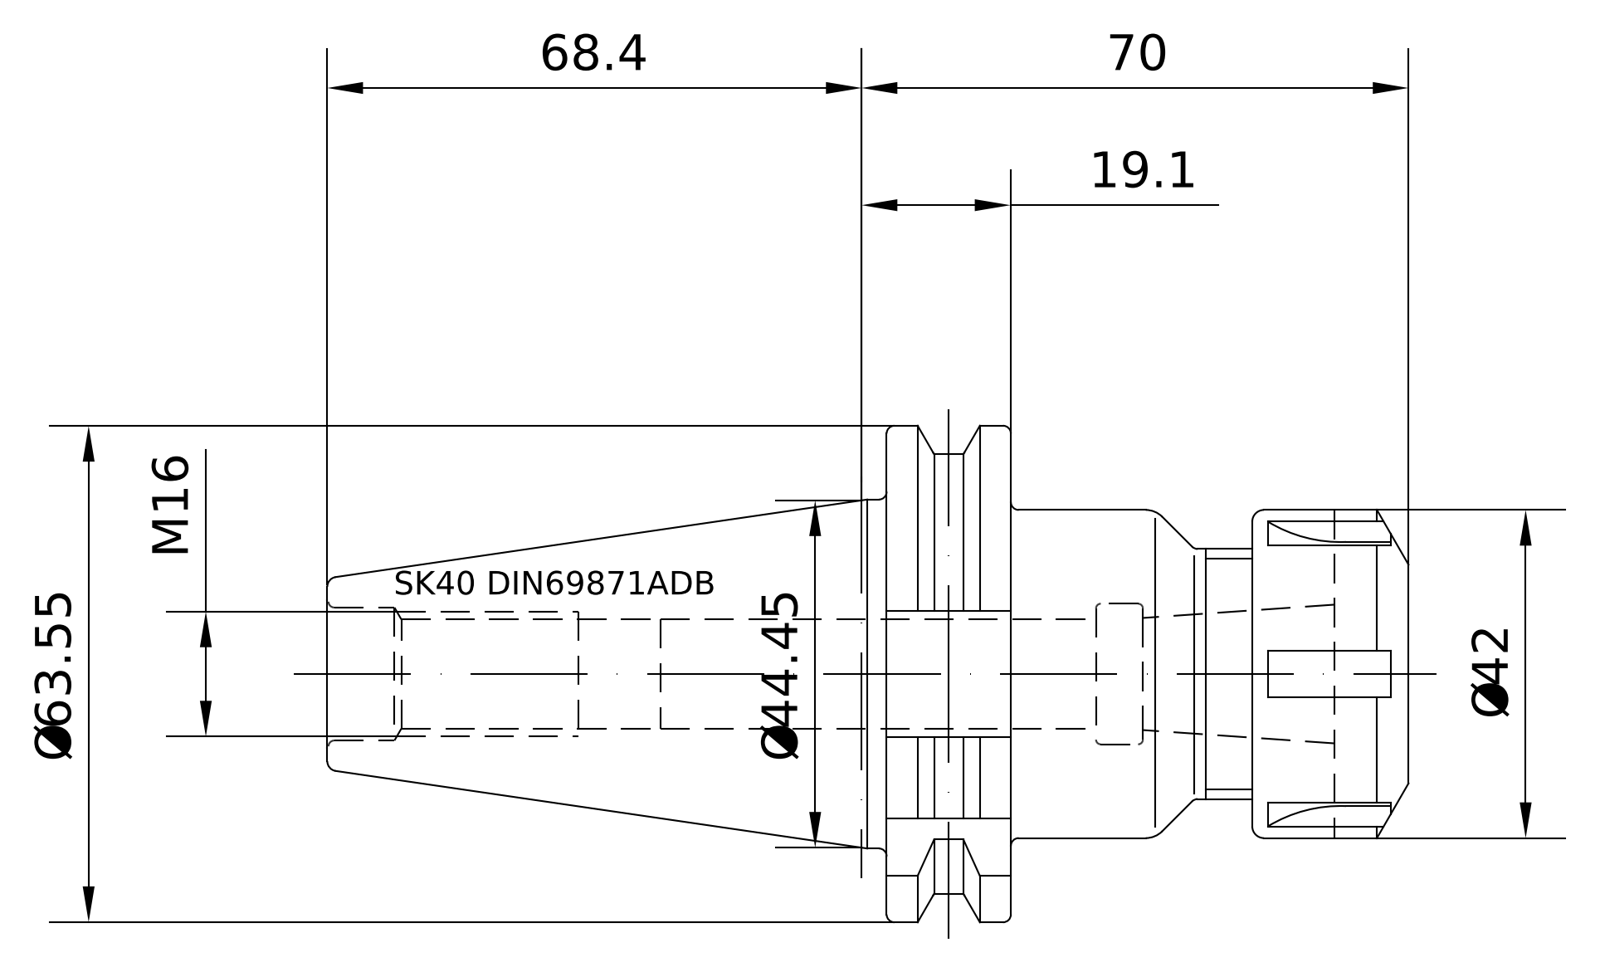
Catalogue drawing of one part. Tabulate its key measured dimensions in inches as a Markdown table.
| quantity | value |
| --- | --- |
| part name | 40-320-25; 83-912-25; 40-320-25_ASM |
| STEP written by | PRO/ENGINEER BY PARAMETRIC TECHNOLOGY CORPORATION, 2010430 (CONFIG_CONTROL_DESIGN) |
| units | inches |
| bodies | 2 solids, 143 faces (41 planar, 28 cylindrical, 74 other) |
| overall size | 5.443 × 2.501 × 2.418 |
| volume | 9.723 in³ |
| surface area | 49.84 in² |
| round holes (diameter × count) | 0.545 × 1, 0.67 × 1, 0.689 × 1, 0.709 × 1 |
| round bosses / shafts (diameter × count) | 1.722 × 1, 1.654 × 1, 1.26 × 1, 0.63 × 1 |
| partial cylindrical surfaces (radius × count) | 0.053 × 1, 1.102 × 1, 1.25 × 1 |
| main face-to-face distances | 1.219, 0.624, 1.843, 2.63, 2.006, 0.787, 2.157, 1.533, 0.315, 0.472 |
